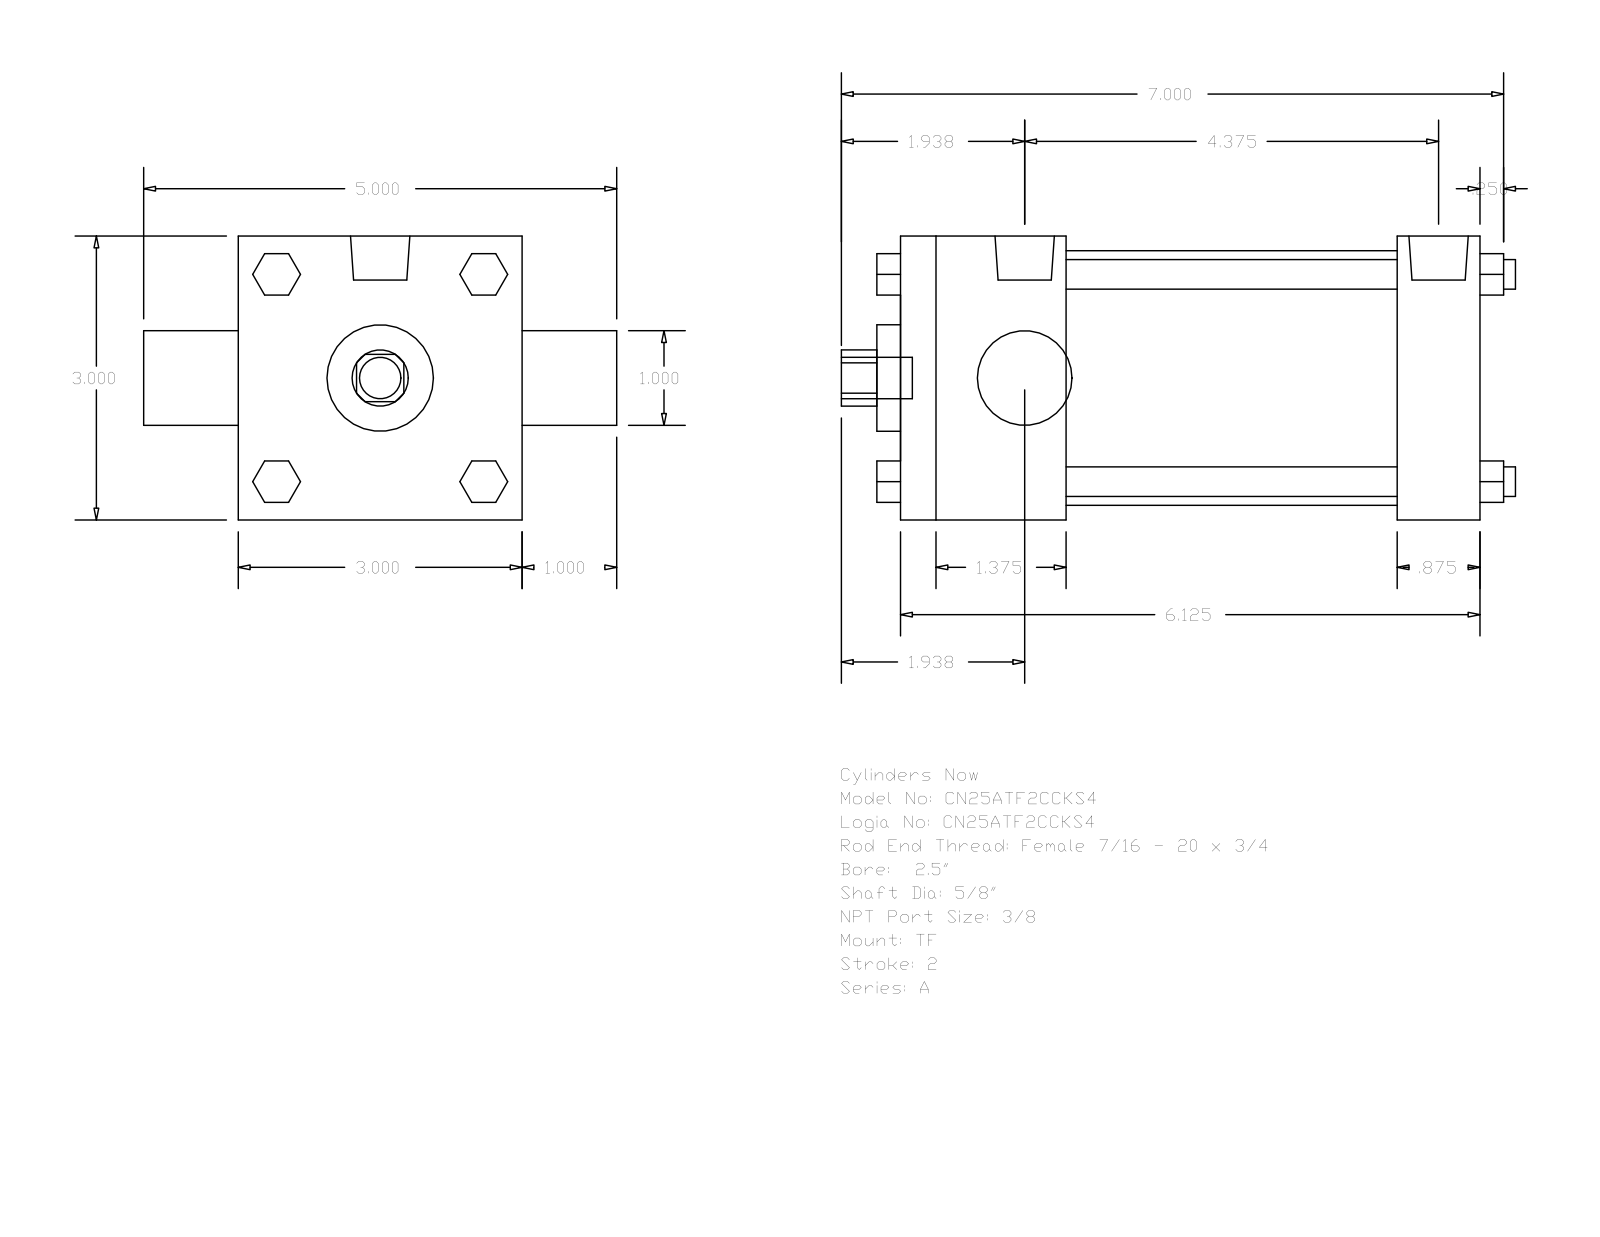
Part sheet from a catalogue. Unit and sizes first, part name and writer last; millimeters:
Units: millimetres
Overall size (bounding box): 180.97 × 127 × 76.2
Round holes (diameter × count): ⌀15.88 ×1, ⌀25.4 ×1, ⌀28.57 ×1, ⌀68.33 ×1
Round bosses / shafts (diameter × count): ⌀7.94 ×4, ⌀5.56 ×3, ⌀15.93 ×2, ⌀11.11 ×1
Partial cylindrical surfaces — rounded edges, fillets, slot ends (radius × count): R7.54 ×1
Main face-to-face distances: 76.2, 155.57, 44.45, 133.34, 88.89, 111.12, 22.23, 25.4, 101.6, 161.92
Bodies: 0 solids, 120 faces (92 planar, 28 cylindrical, 0 other)
Part name (STEP PRODUCT): A_TF__0250_0.625
STEP written by: GSSL Pune (CONFIG_CONTROL_DESIGN)
